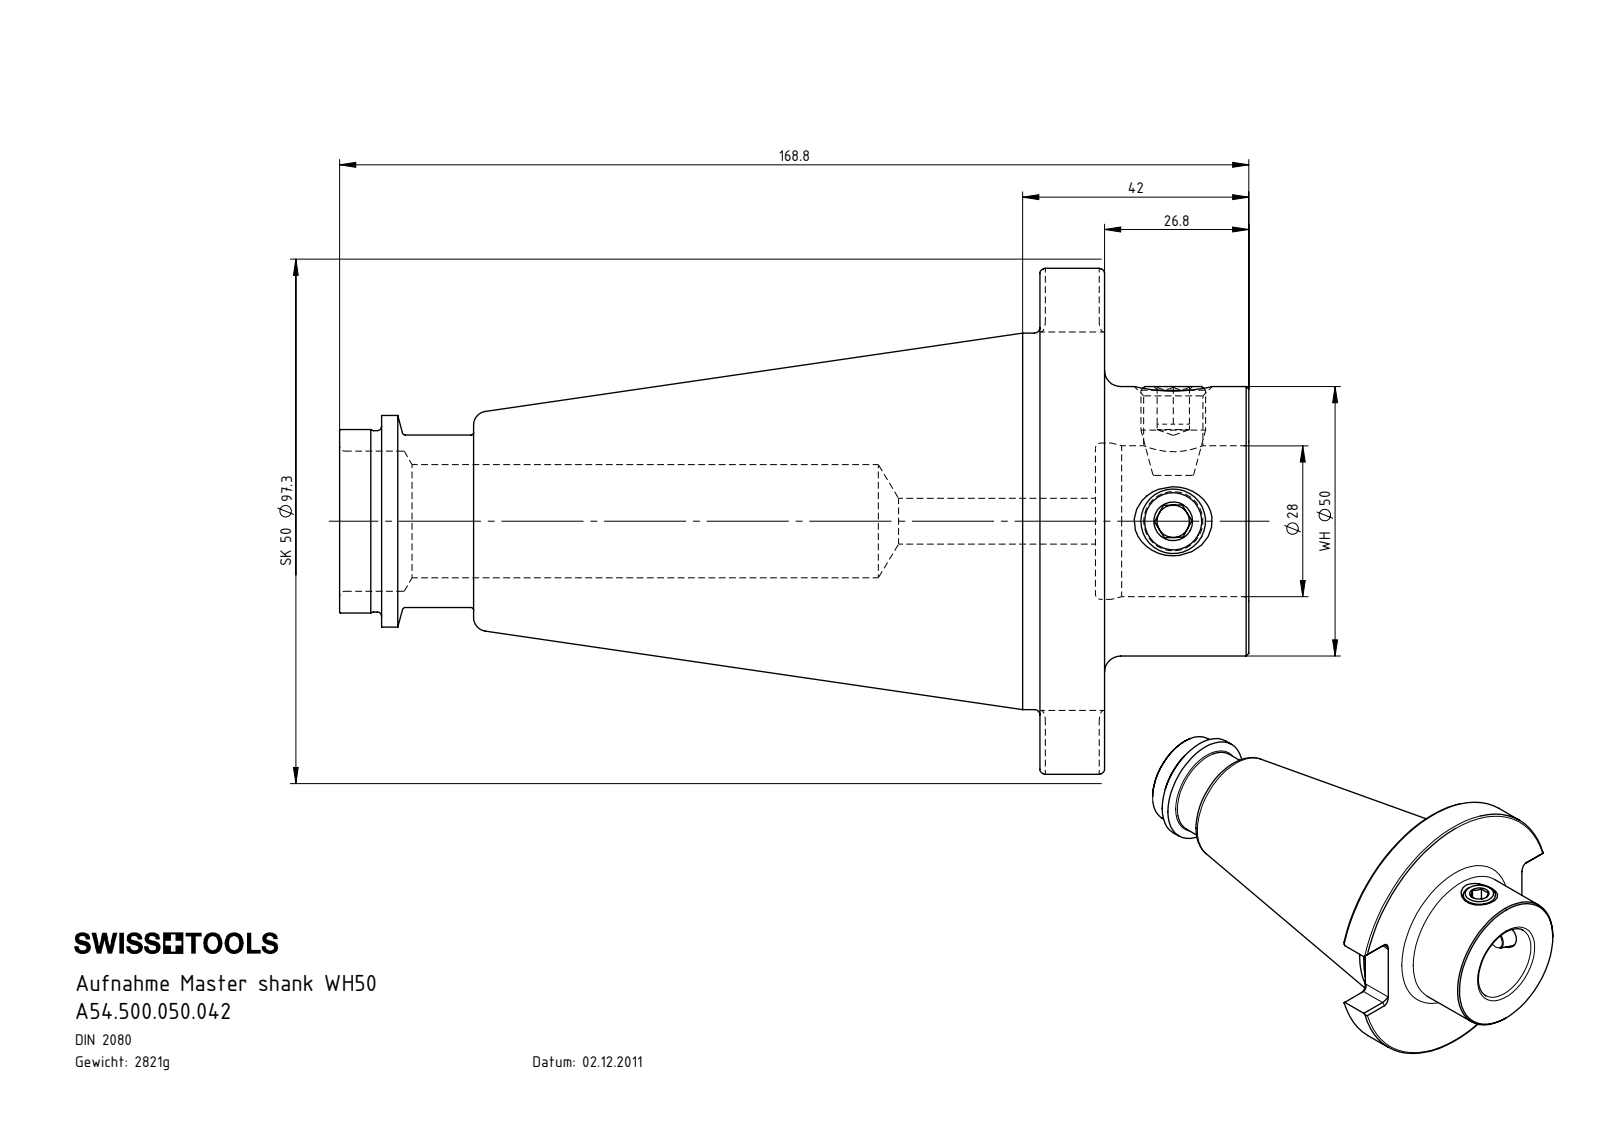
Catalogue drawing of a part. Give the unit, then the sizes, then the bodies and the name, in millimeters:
Units: millimetres
Overall size (bounding box): 168.8 × 97.3 × 93.84
Round holes (diameter × count): ⌀6 ×2, ⌀11 ×2, ⌀8.5 ×1, ⌀21 ×1, ⌀26 ×1, ⌀28 ×1, ⌀29 ×1
Round bosses / shafts (diameter × count): ⌀12 ×2, ⌀97.3 ×1, ⌀69.85 ×1, ⌀50 ×1, ⌀39.24 ×1, ⌀34.05 ×1, ⌀33.65 ×1, ⌀32 ×1
Partial cylindrical surfaces — rounded edges, fillets, slot ends (radius × count): R2 ×12
Main face-to-face distances: 12, 38.8, 26.8, 10.3, 1.7, 28.5, 130, 140.3, 142, 168.8
Volume: 359 350 mm³ · Surface area: 52 735 mm²
Bodies: 3 solids, 166 faces (52 planar, 48 cylindrical, 66 other)
Part name (STEP PRODUCT): WH5-ER1.001.017; SZ5-WH5.K01.042_A; A54.500.050.042
STEP written by: SolidWorks 2022 (CONFIG_CONTROL_DESIGN)
